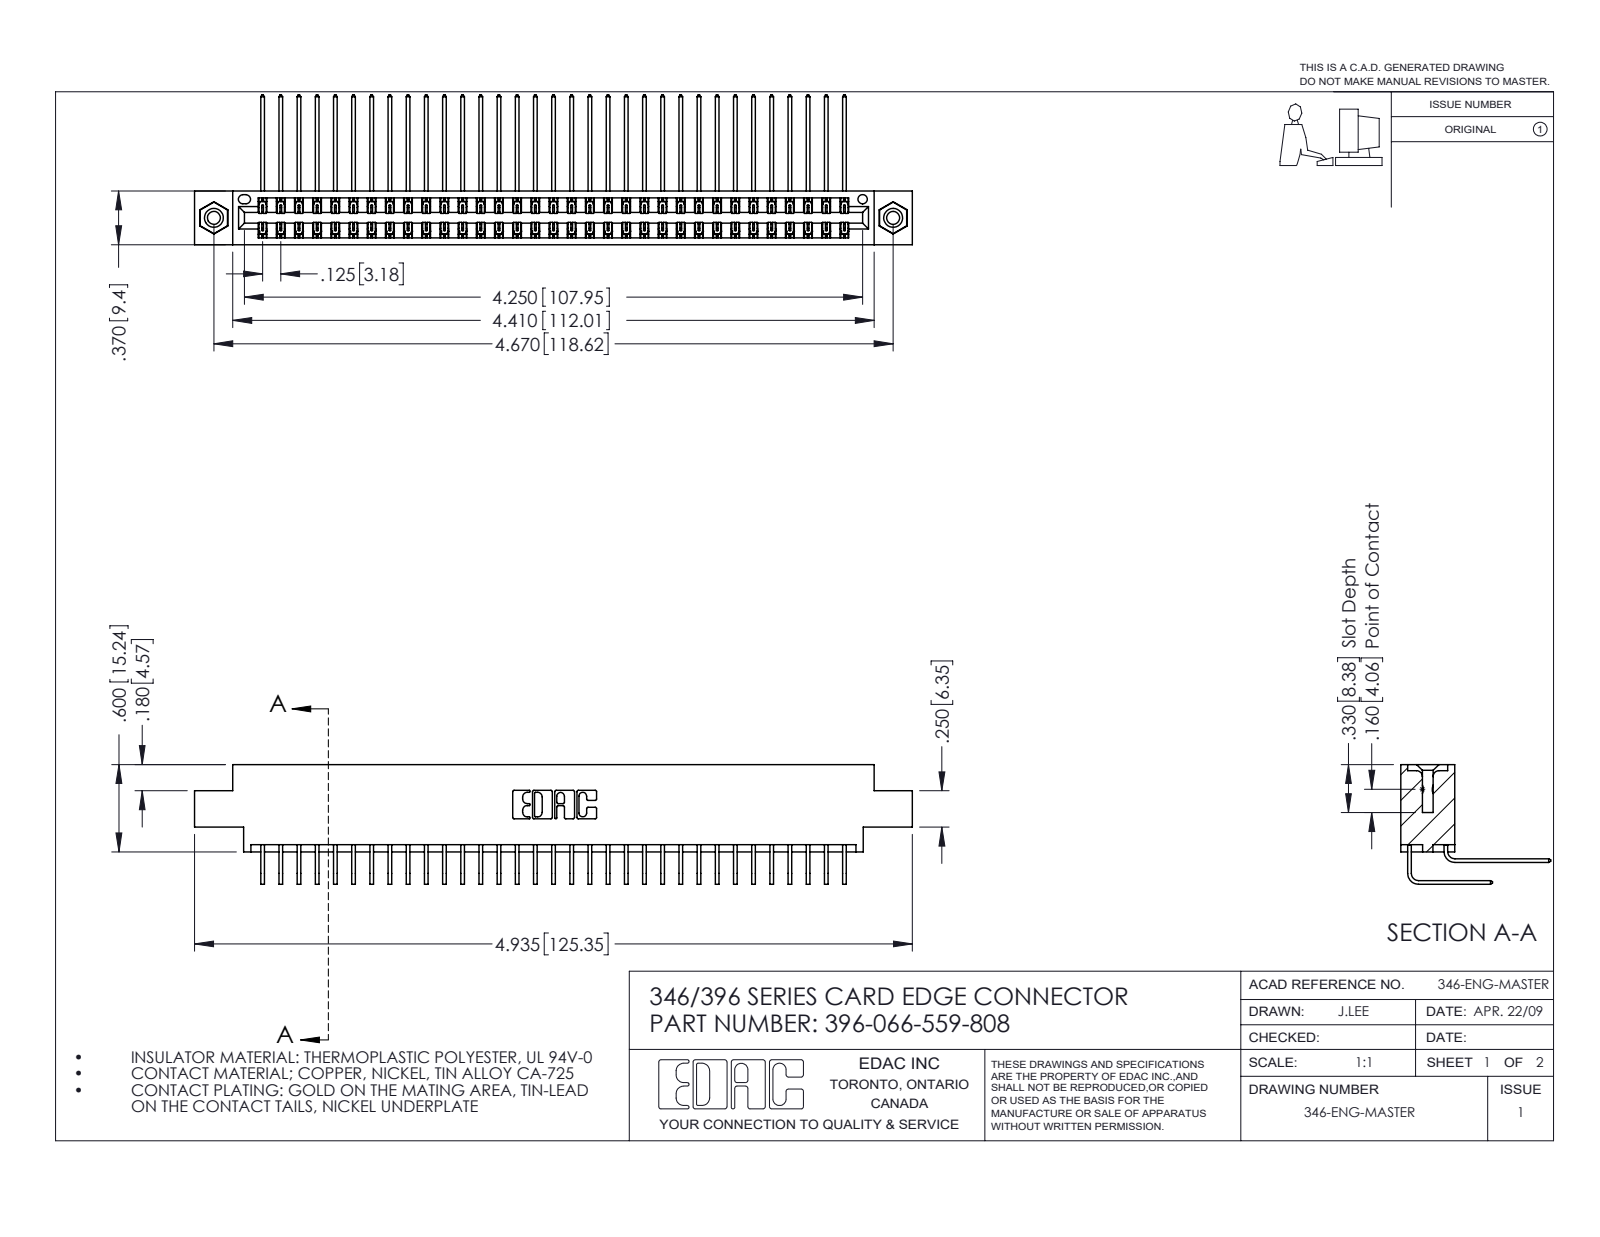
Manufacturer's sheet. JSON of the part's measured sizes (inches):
{"part_name": "345-292-001_558 559 Tail - 1; 396-066-559-808; 345-250-001_345-250-003-102; 346 Part_0.170 Offset - 0.156 Dia-TI (+1 more)", "step_written_by": "SolidWorks 2016 (CONFIG_CONTROL_DESIGN)", "units": "inches", "bodies": {"solids": 69, "faces": 3750, "planar": 2554, "cylindrical": 1180, "other": 16}, "overall_size": [4.935, 1.03, 0.823], "volume_in3": 0.755, "surface_area_in2": 29.28, "round_holes": [[0.089, 2], [0.125, 2], [0.156, 2], [0.064, 1]], "round_bosses_or_shafts": [[0.155, 2]], "partial_cylinders_radius": [[0.006, 99], [0.01, 22], [0.007, 6], [0.031, 6], [0.026, 3], [0.014, 2], [0.022, 2], [0.024, 2]], "face_to_face_distances": [0.048, 0.322, 0.025, 0.37, 0.25, 0.072, 0.298, 0.275, 0.222, 0.148], "hole_center_spacings": [0.246, 4.462, 4.67]}
